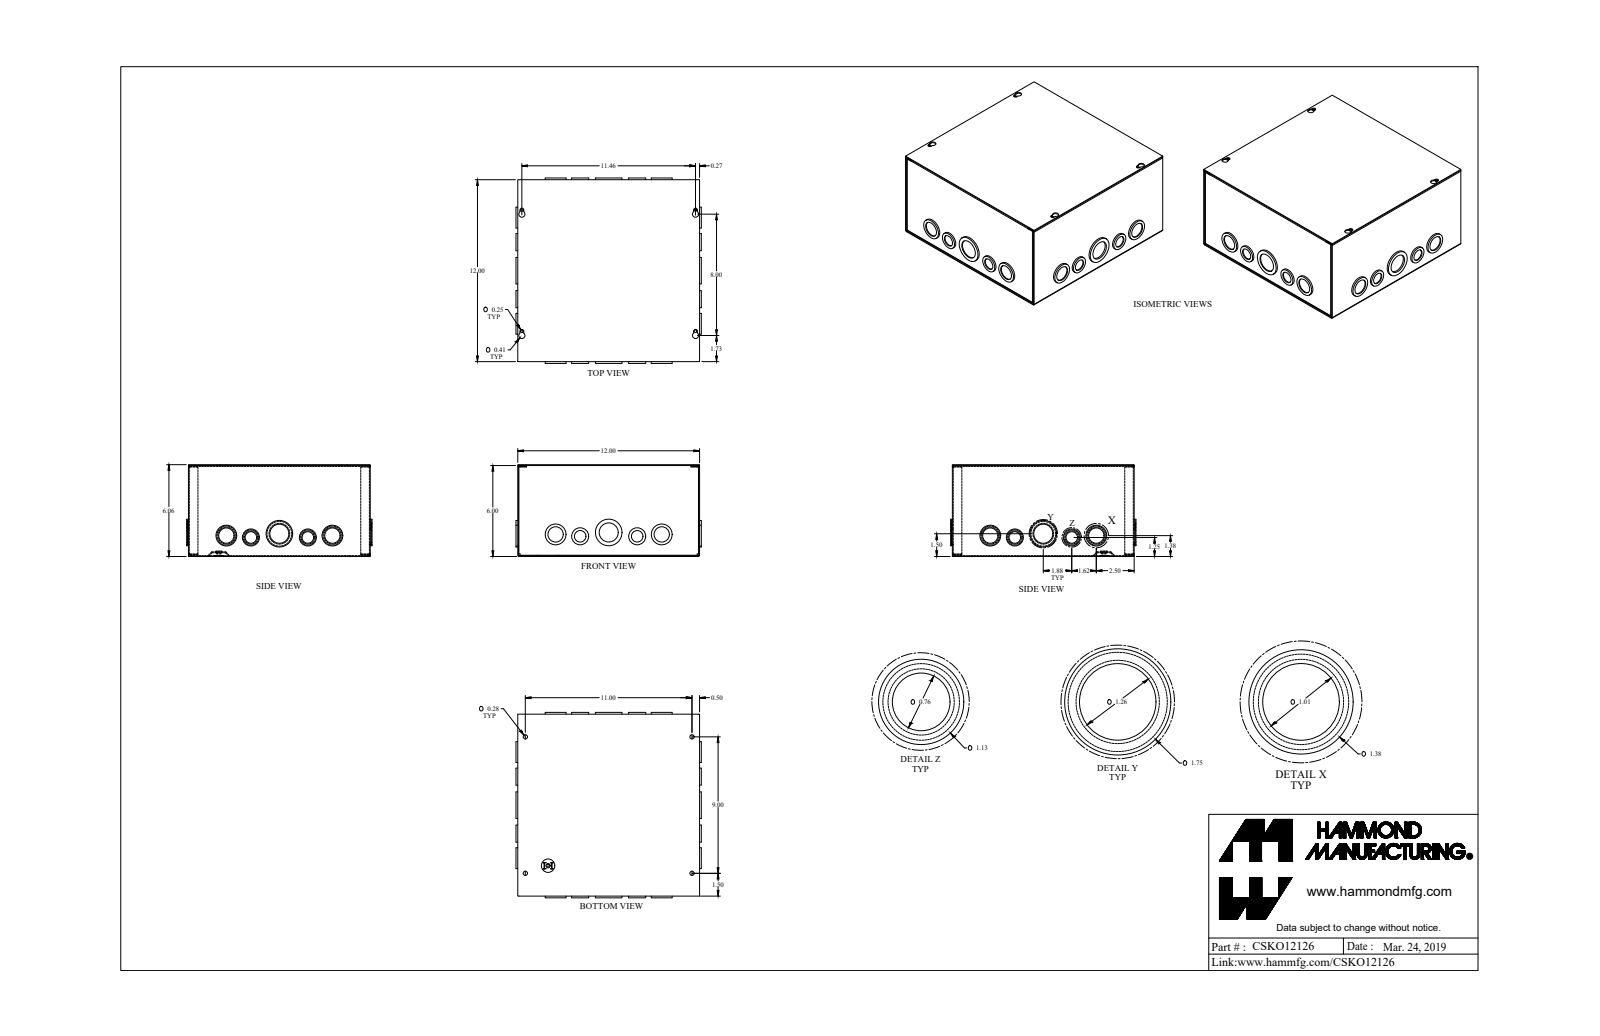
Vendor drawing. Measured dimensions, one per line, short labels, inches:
name: CSKO12126_Default
written by: SolidWorks 2019 (CONFIG_CONTROL_DESIGN)
unit: in
bodies: 4 solids, 445 faces (205 planar, 232 cylindrical, 8 other)
size: 12.234 × 12.234 × 6.057
volume: 35.78 in³; area: 1 268 in²
holes: 8× ⌀1.011, 6× ⌀1.261, 5× ⌀0.17, 4× ⌀0.281, 4× ⌀0.761, 2× ⌀1.636, 1× ⌀0.5
bosses: 6× ⌀1.125, 5× ⌀1.375, 4× ⌀0.875, 4× ⌀0.875, 3× ⌀1.375, 2× ⌀1.75, 2× ⌀1.125, 1× ⌀0.492
rounds: 12× R0.029, 12× R0.086, 8× R0.057, 4× R0.125, 4× R0.203
face distances: 0.057, 6, 11.943, 5.943, 12, 6.057, 11.886, 0.114, 0.08, 5.863
hole spacings: 0.55, 1.625, 1.896, 3.502, 5.381, 8.503, 11.241, 14.084
